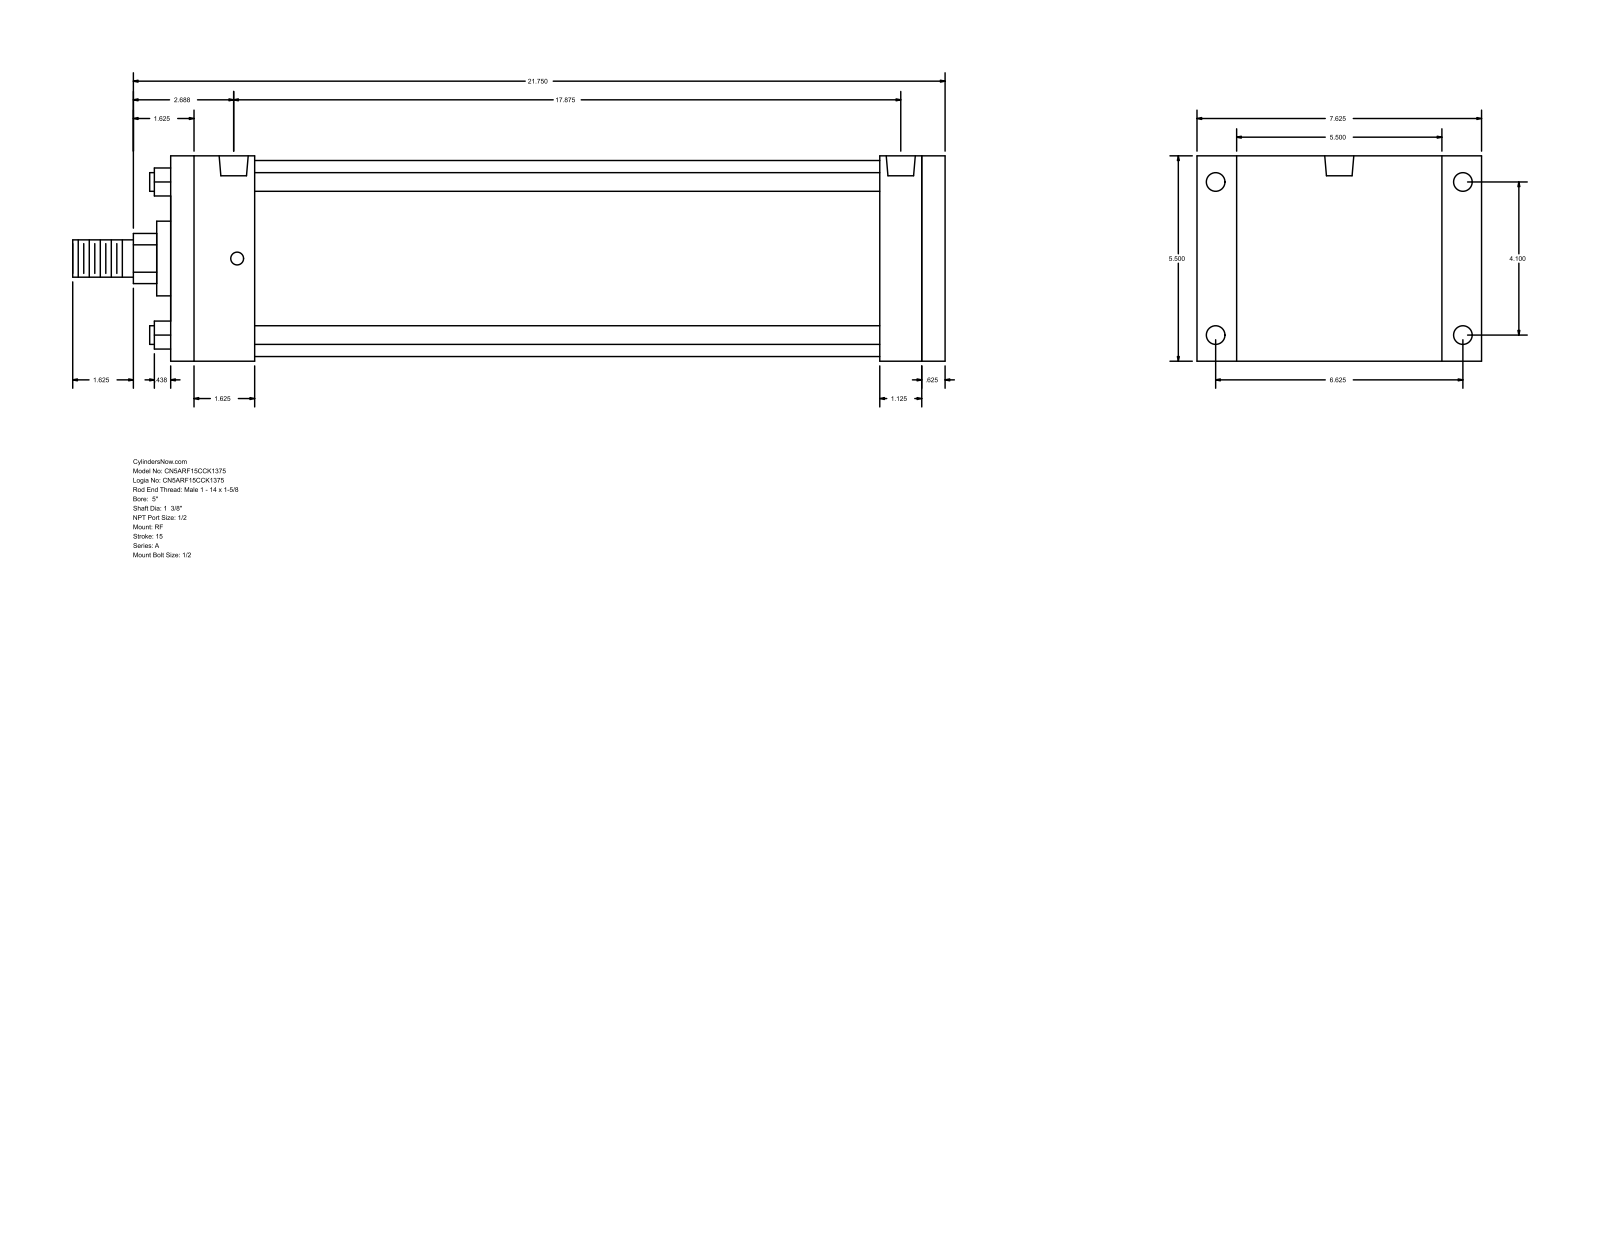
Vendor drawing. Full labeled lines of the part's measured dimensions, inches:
Part name (STEP PRODUCT): A_RF__0500_1.375
STEP written by: GSSL Pune (CONFIG_CONTROL_DESIGN)
Units: inches
Bodies: 0 solids, 92 faces (64 planar, 28 cylindrical, 0 other)
Overall size (bounding box): 23.375 × 7.625 × 5.5
Round holes (diameter × count): ⌀0.344 ×4, ⌀0.5 ×4, ⌀0.778 ×2
Round bosses / shafts (diameter × count): ⌀0.5 ×4, ⌀5.25 ×1, ⌀2 ×1, ⌀1.375 ×1, ⌀1 ×1
Partial cylindrical surfaces — rounded edges, fillets, slot ends (radius × count): R0.672 ×1
Main face-to-face distances: 5.5, 20.75, 20.125, 0.625, 2.25, 1.125, 17.875, 18.5, 19, 16.75
Hole centre spacings: 0.094, 4.1, 6.625, 7.791, 17.687, 17.781, 17.875
